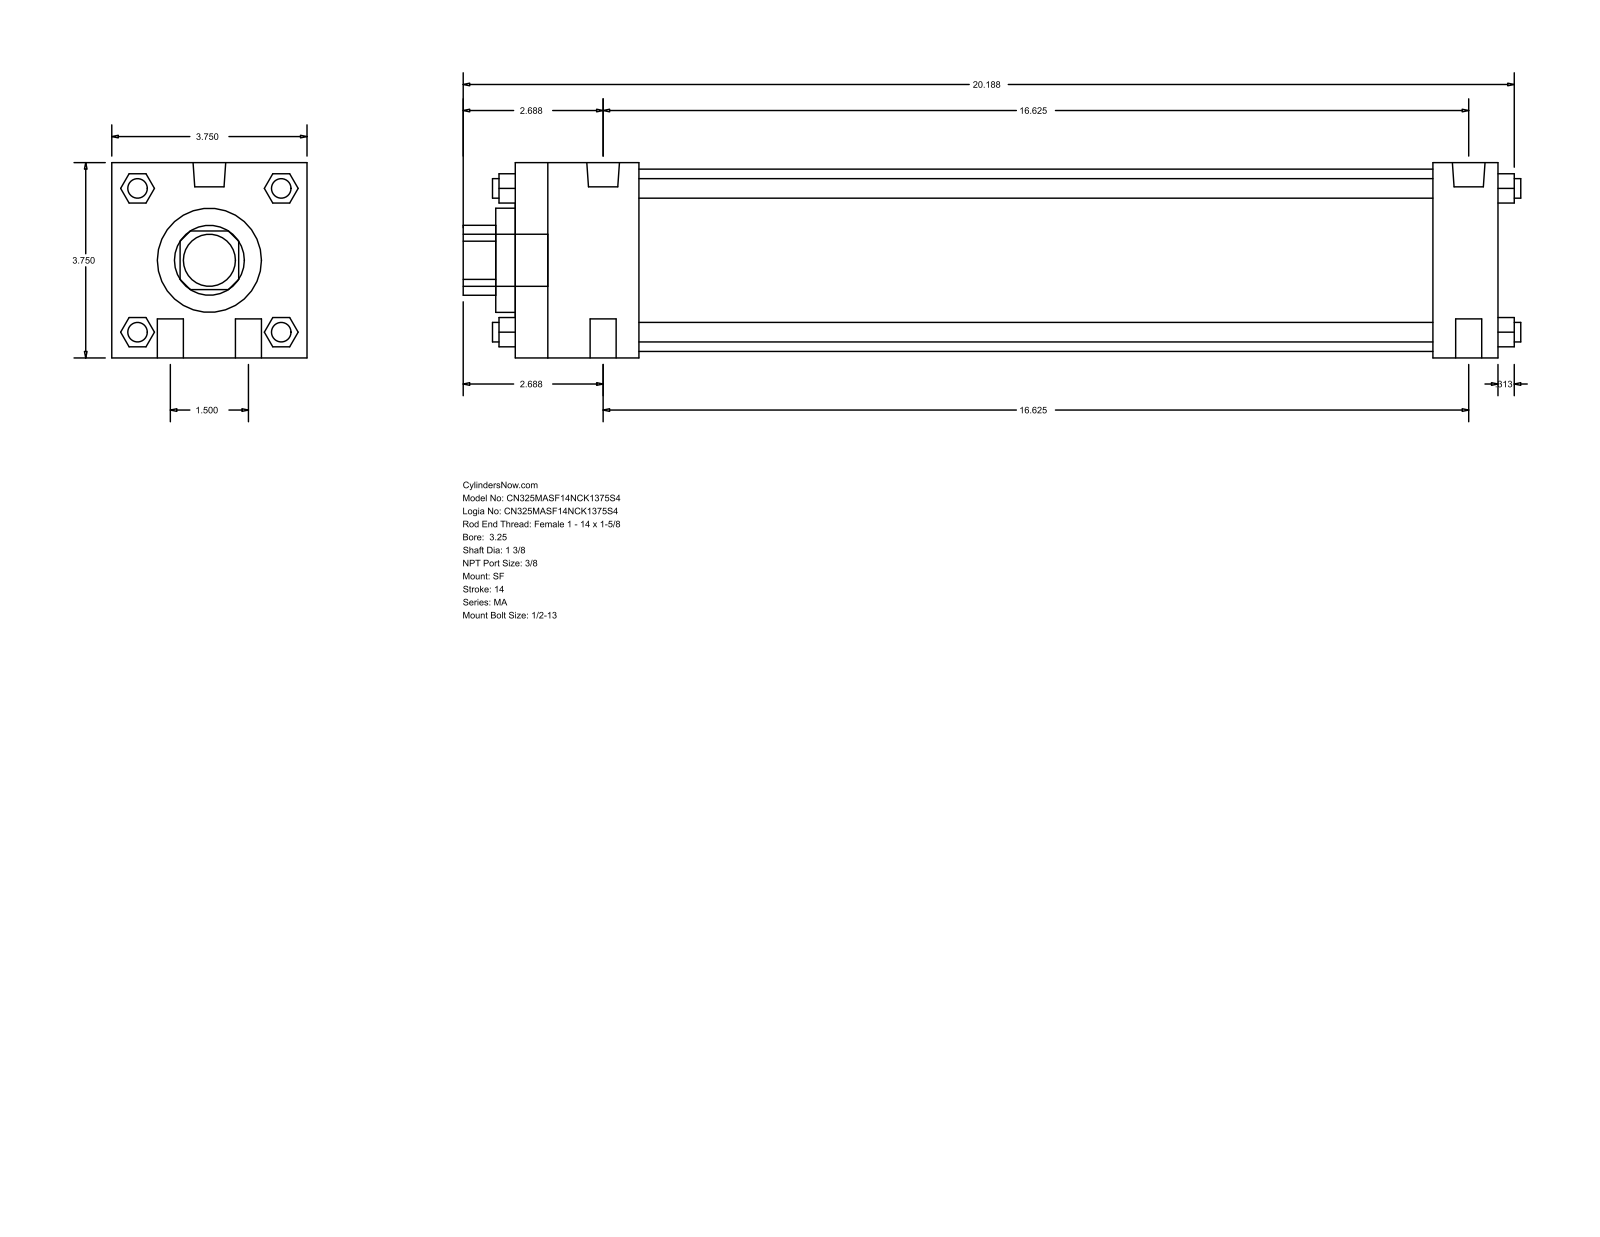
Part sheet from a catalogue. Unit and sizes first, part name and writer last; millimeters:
Units: millimetres
Overall size (bounding box): 515.94 × 95.25 × 95.25
Round holes (diameter × count): ⌀34.92 ×1, ⌀50.8 ×1, ⌀88.9 ×1
Round bosses / shafts (diameter × count): ⌀12.7 ×4, ⌀9.53 ×4, ⌀15.93 ×2, ⌀11.11 ×2, ⌀25.4 ×1
Partial cylindrical surfaces — rounded edges, fillets, slot ends (radius × count): R17.06 ×1
Main face-to-face distances: 95.24, 479.42, 447.67, 31.75, 60.32, 387.35, 419.1, 9.52, 69.84, 457.19
Bodies: 0 solids, 124 faces (94 planar, 30 cylindrical, 0 other)
Part name (STEP PRODUCT): MA_SF__0325_1.375
STEP written by: GSSL Pune (CONFIG_CONTROL_DESIGN)
